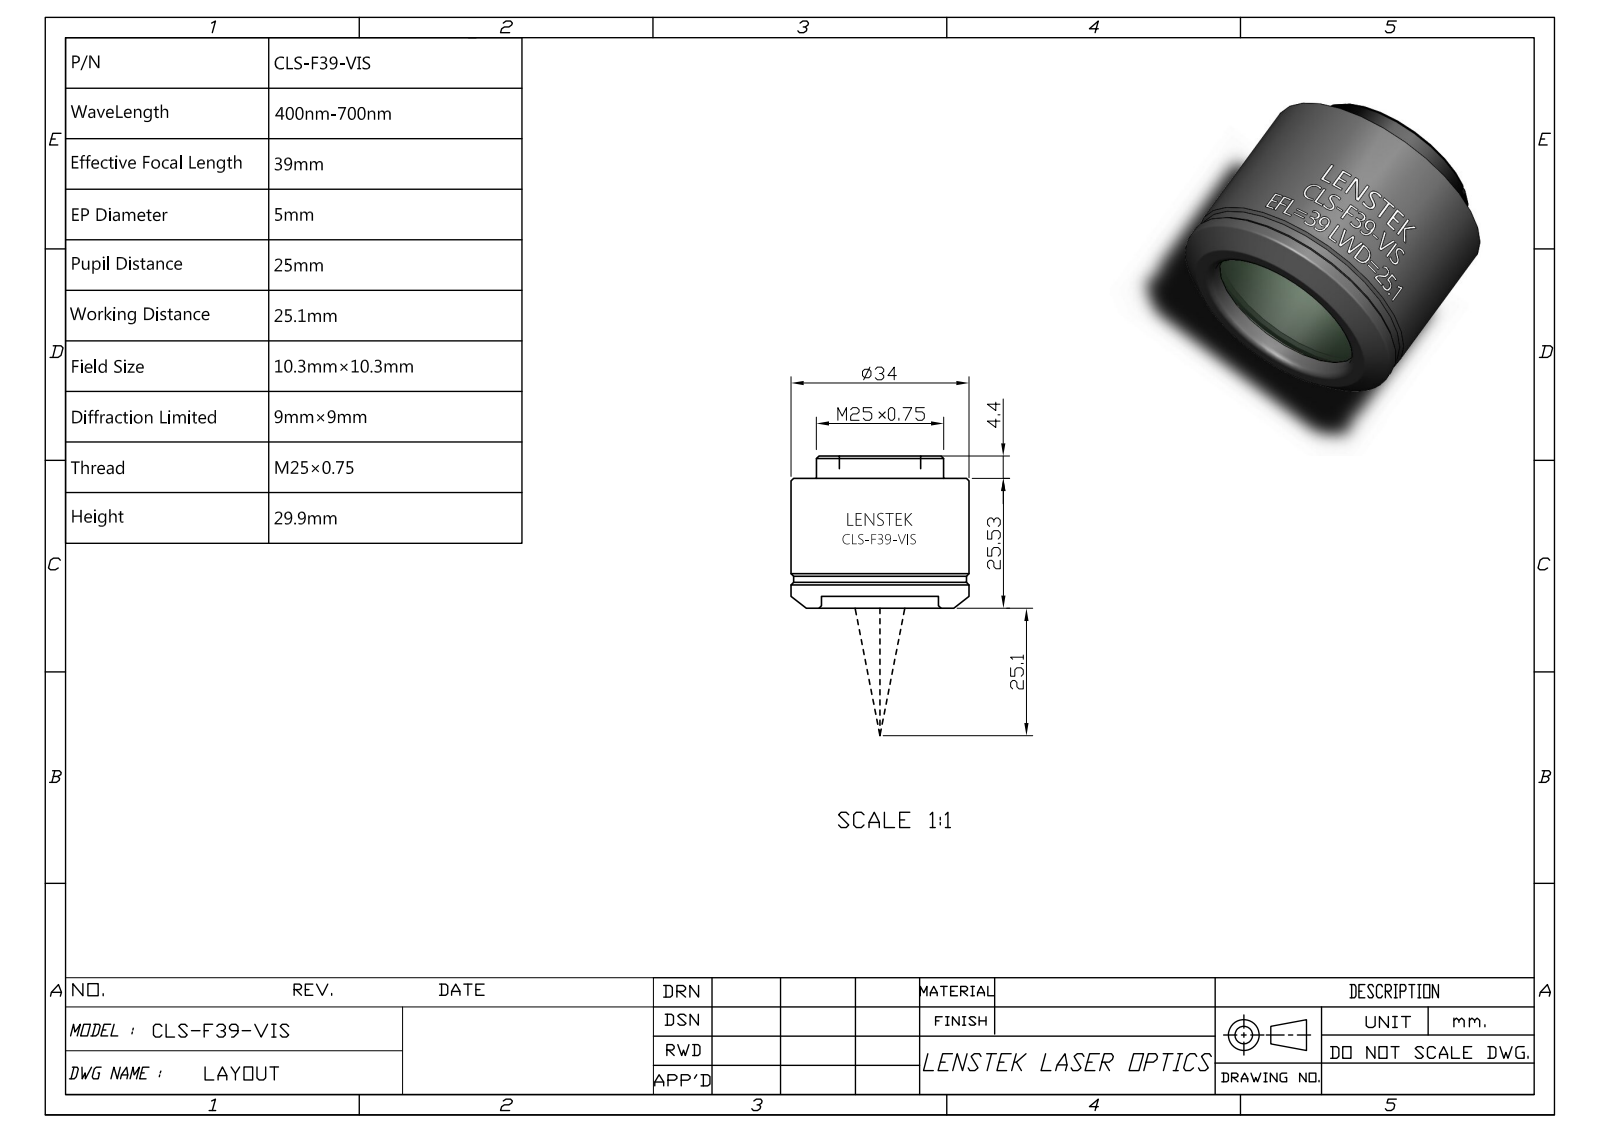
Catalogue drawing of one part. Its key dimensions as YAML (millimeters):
part_name: "CLS-F39-VIS"
step_written_by: "SolidWorks 2018 (AUTOMOTIVE_DESIGN)"
units: millimeters
bodies: {solids: 5, faces: 449, planar: 220, cylindrical: 56, other: 173}
overall_size: [34, 34, 30]
volume: 13600
surface_area: 14006
round_holes:
  - {diameter: 16, count: 1}
  - {diameter: 18.5, count: 1}
  - {diameter: 23, count: 1}
  - {diameter: 25.5, count: 1}
  - {diameter: 26, count: 1}
  - {diameter: 30, count: 1}
  - {diameter: 31.5, count: 1}
round_bosses_or_shafts:
  - {diameter: 34, count: 1}
  - {diameter: 33.2, count: 1}
  - {diameter: 31, count: 1}
  - {diameter: 29.99, count: 1}
  - {diameter: 29, count: 1}
  - {diameter: 25, count: 1}
  - {diameter: 24, count: 1}
  - {diameter: 18, count: 1}
partial_cylinders:
  - {radius: 16.99, count: 1}
face_to_face_distances: [22.65, 3.7, 18.95, 7.5, 3.8, 15.15, 12, 23.15, 19.45, 15.65]
